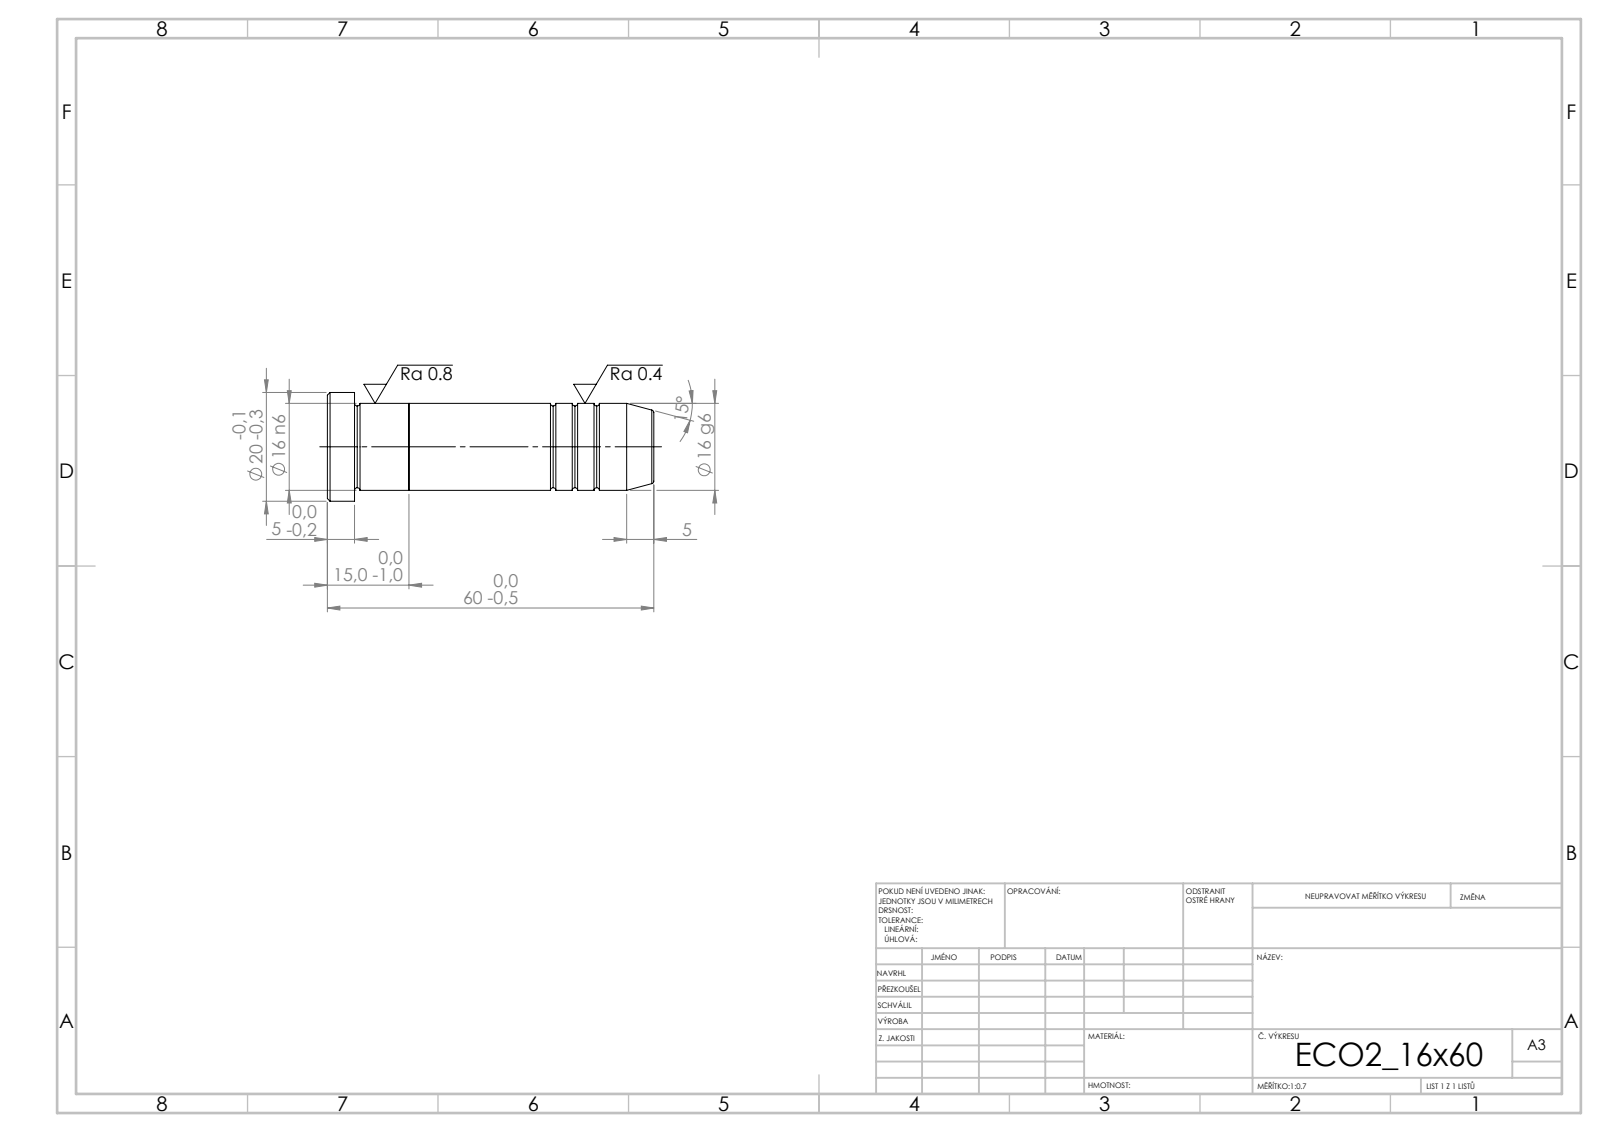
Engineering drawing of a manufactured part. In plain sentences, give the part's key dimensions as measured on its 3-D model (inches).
Its 3-D file was written by "SolidWorks 2019 (CONFIG_CONTROL_DESIGN)". It is 2 solids with 39 faces: 5 planar, 12 cylindrical and 22 other. Overall it measures 2.362 by 0.787 by 0.787 inches. Its volume is 0.756 cubic inches and its surface area 6.375 square inches. Round bosses or shafts: 1 of diameter 0.787, 1 of diameter 0.63. The main face-to-face distances are 0.591, 1.772, 2.362, 2.165, 0.394, 0.197.
